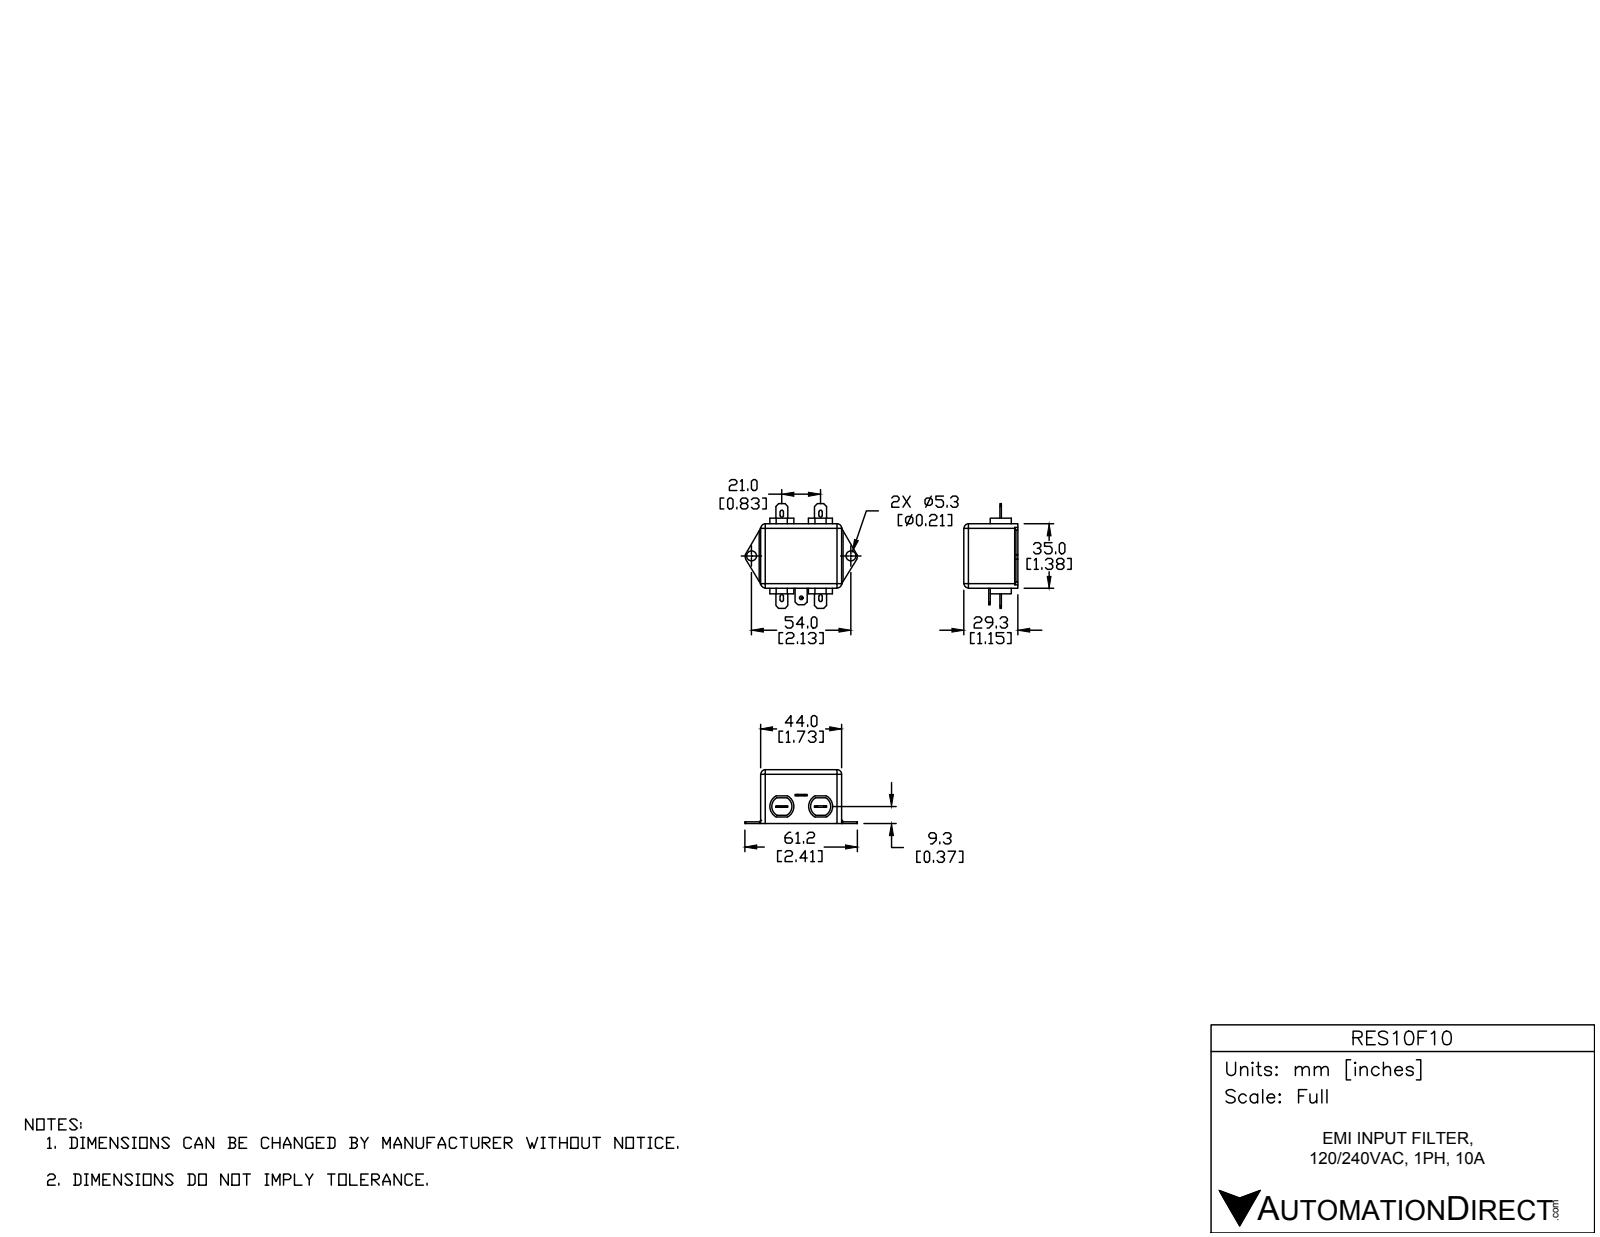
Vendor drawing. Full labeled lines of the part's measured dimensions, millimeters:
Part name (STEP PRODUCT): RES10F10
STEP written by: SolidWorks 2015 (AUTOMOTIVE_DESIGN)
Units: millimetres
Bodies: 1 solid, 137 faces (79 planar, 54 cylindrical, 4 other)
Overall size (bounding box): 62.99 × 56.8 × 29.3
Volume: 46 184 mm³ · Surface area: 9 278 mm²
Round holes (diameter × count): ⌀5.3 ×2, ⌀2 ×1
Partial cylindrical surfaces — rounded edges, fillets, slot ends (radius × count): R2.5 ×10, R0.9 ×8, R0.75 ×2, R5.5 ×2, R6.5 ×2
Main face-to-face distances: 29.3, 35, 44, 1.4, 36.4, 1, 0.8, 7.9, 8.9, 20.4
Hole centre spacings: 35.34, 54
